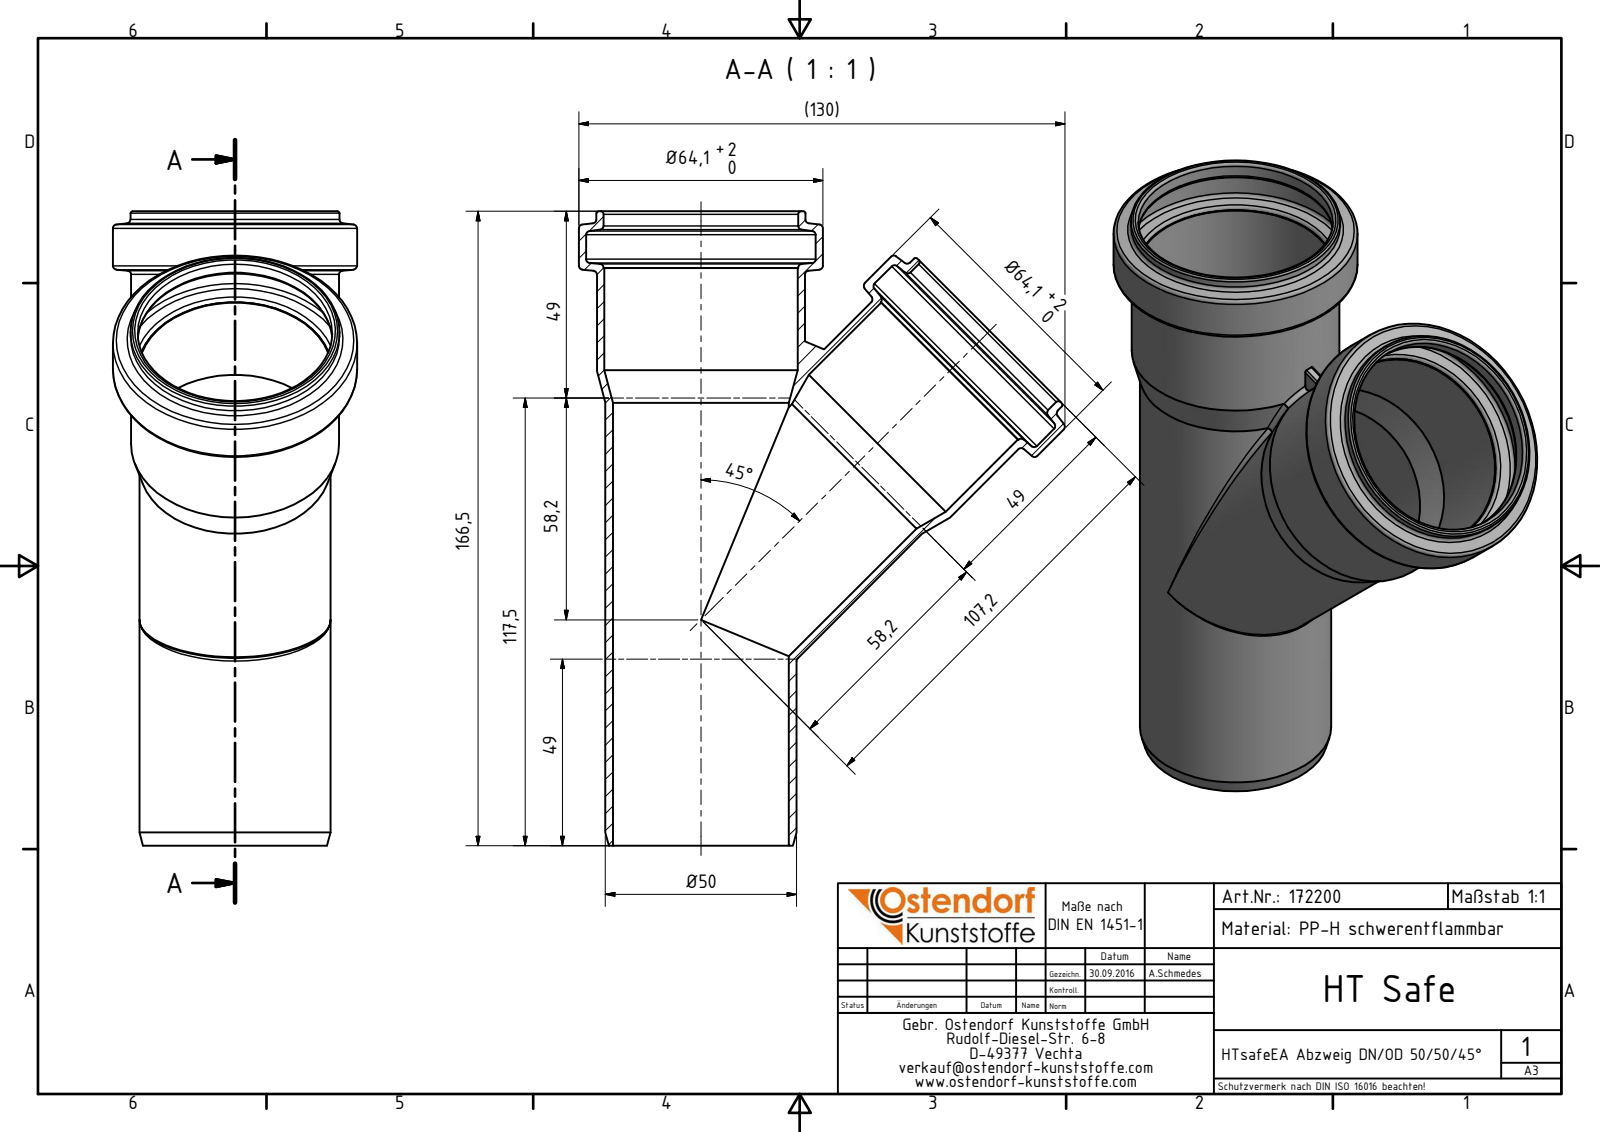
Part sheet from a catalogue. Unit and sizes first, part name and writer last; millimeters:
Units: millimetres
Overall size (bounding box): 166.5 × 127.64 × 64.1
Round holes (diameter × count): ⌀51.1 ×3, ⌀46.2 ×2, ⌀50.8 ×2, ⌀60.3 ×2
Round bosses / shafts (diameter × count): ⌀64.1 ×2, ⌀54.9 ×2, ⌀54.6 ×2, ⌀50.2 ×2
Partial cylindrical surfaces — rounded edges, fillets, slot ends (radius × count): R0.5 ×2
Main face-to-face distances: 166.5, 151.6, 14.9, 14.89, 2.8
Volume: 77 502 mm³ · Surface area: 79 257 mm²
Bodies: 1 solid, 68 faces (8 planar, 20 cylindrical, 40 other)
Part name (STEP PRODUCT): 172200 HTsafeEA DN_OD 50_50_45°
STEP written by: Autodesk Inventor 2016 (AUTOMOTIVE_DESIGN)
